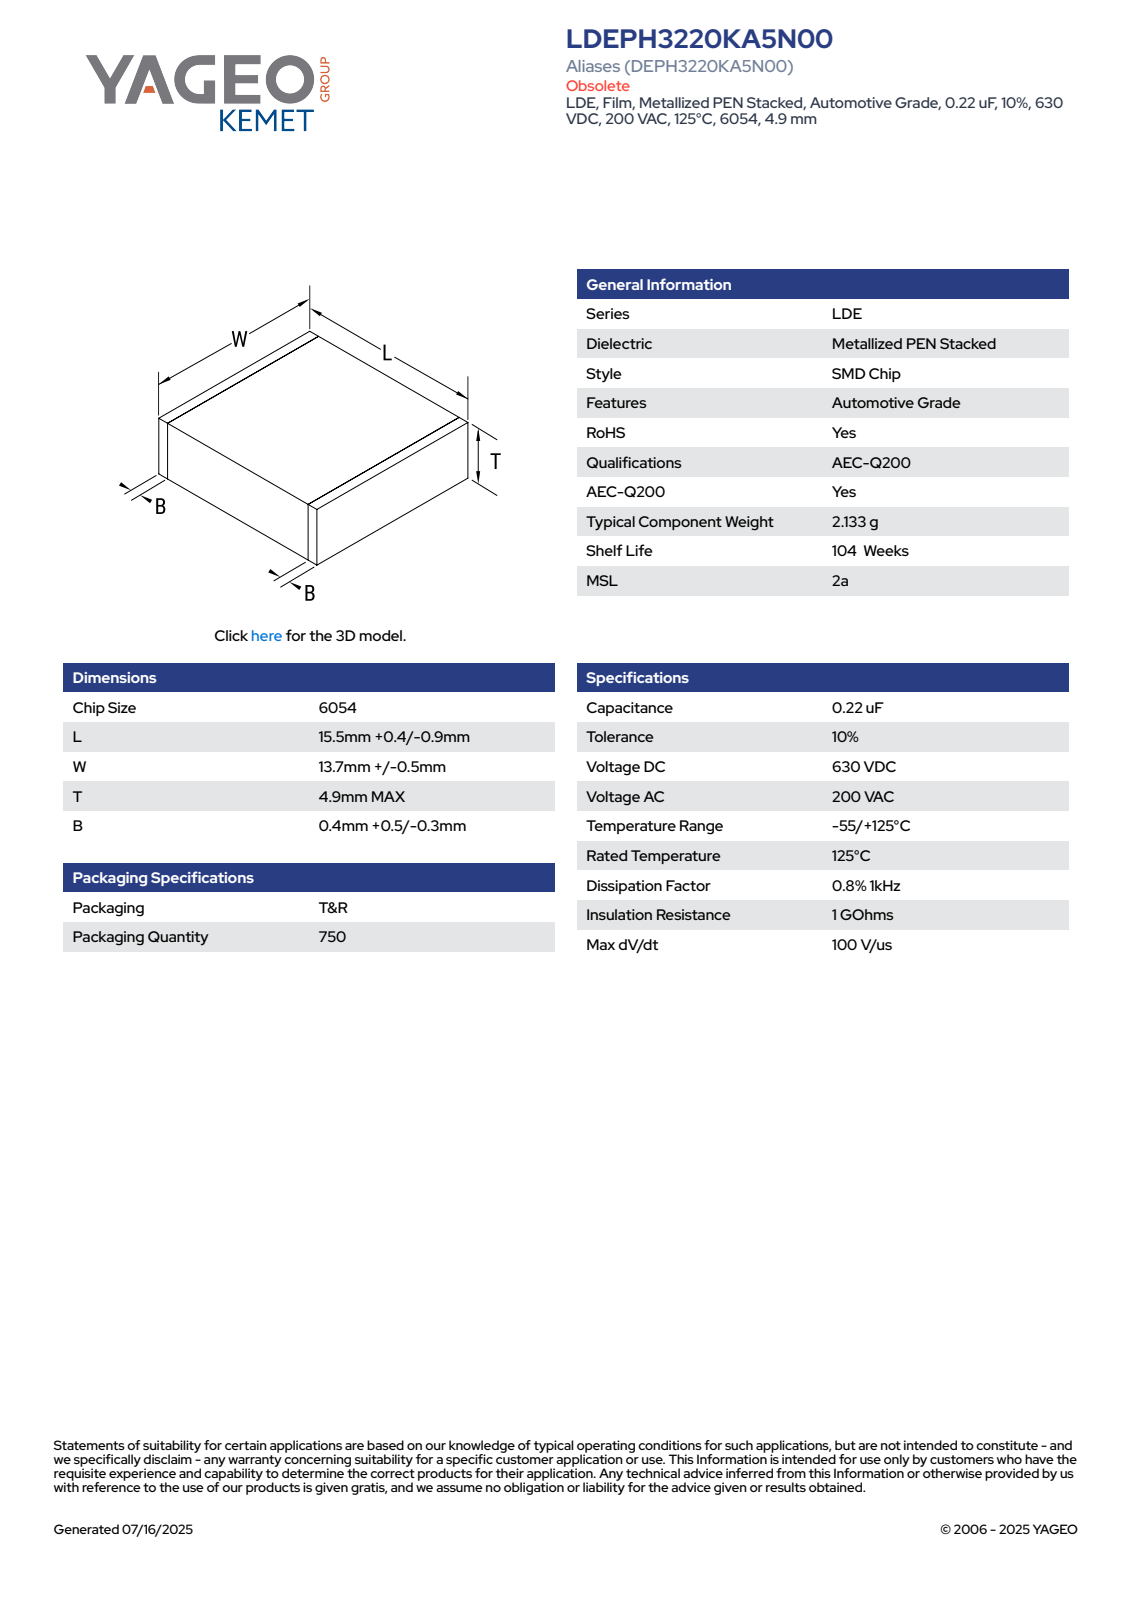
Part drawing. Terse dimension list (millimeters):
name: CFS_LDELDB_6054_L15.9W14.2T4.9B0.9
written by: SolidWorks 2020 (AUTOMOTIVE_DESIGN)
unit: mm
bodies: 4 solids, 73 faces (73 planar, 0 cylindrical, 0 other)
size: 15.9 × 14.2 × 4.9
volume: 1 101 mm³; area: 758 mm²
face distances: 4.88, 14.18, 15.9, 4.89, 4.9, 14.19, 14.2, 0.5, 15.4, 14.9
